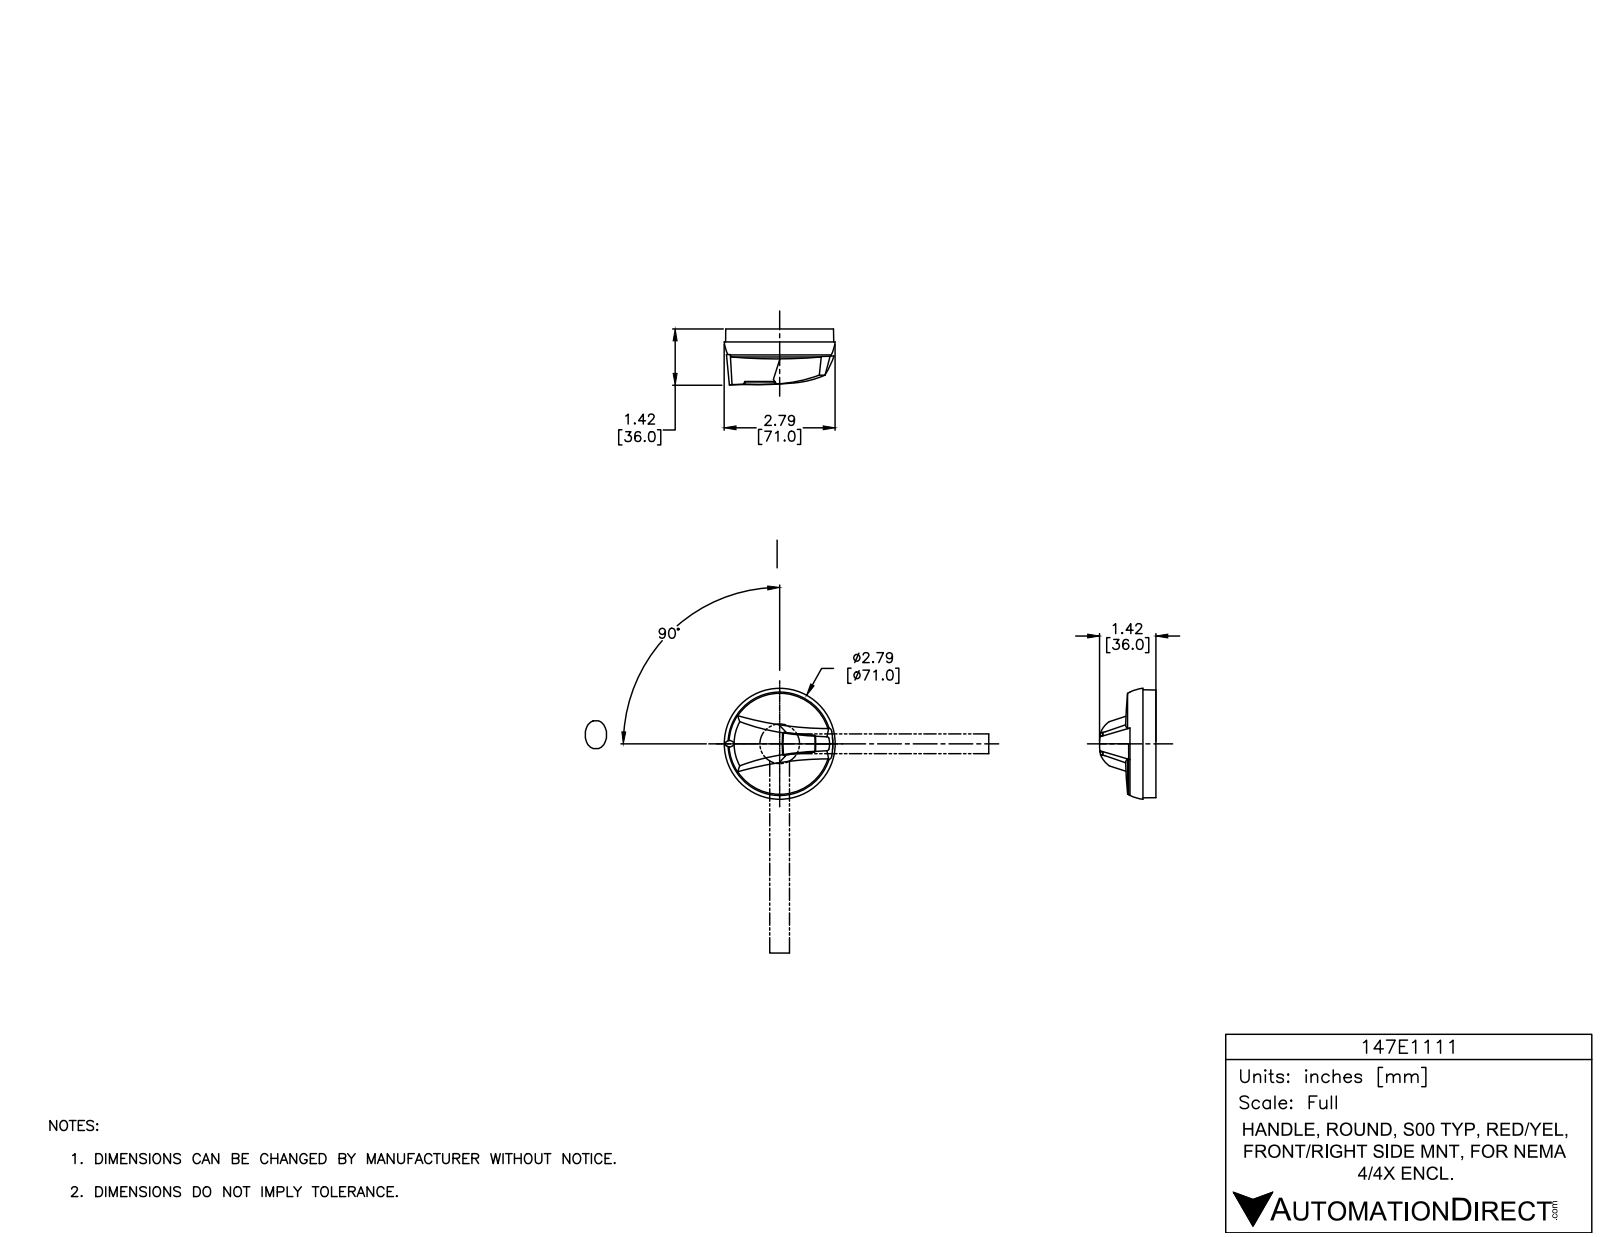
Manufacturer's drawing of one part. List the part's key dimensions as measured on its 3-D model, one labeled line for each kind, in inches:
Part name (STEP PRODUCT): 147E1111
STEP written by: SolidWorks 2015 (AUTOMOTIVE_DESIGN)
Units: inches
Bodies: 1 solid, 76 faces (29 planar, 14 cylindrical, 33 other)
Overall size (bounding box): 2.8 × 2.8 × 1.899
Volume: 5.42 in³ · Surface area: 24.86 in²
Round holes (diameter × count): ⌀0.169 ×4, ⌀0.457 ×1, ⌀2.618 ×1
Round bosses / shafts (diameter × count): ⌀0.801 ×1
Main face-to-face distances: 0.624, 0.616, 0.03, 0.646, 0.654, 0.488, 0.518, 1.134, 1.142, 0.807
Hole centre spacings: 0.961, 1.102, 1.575, 1.922
